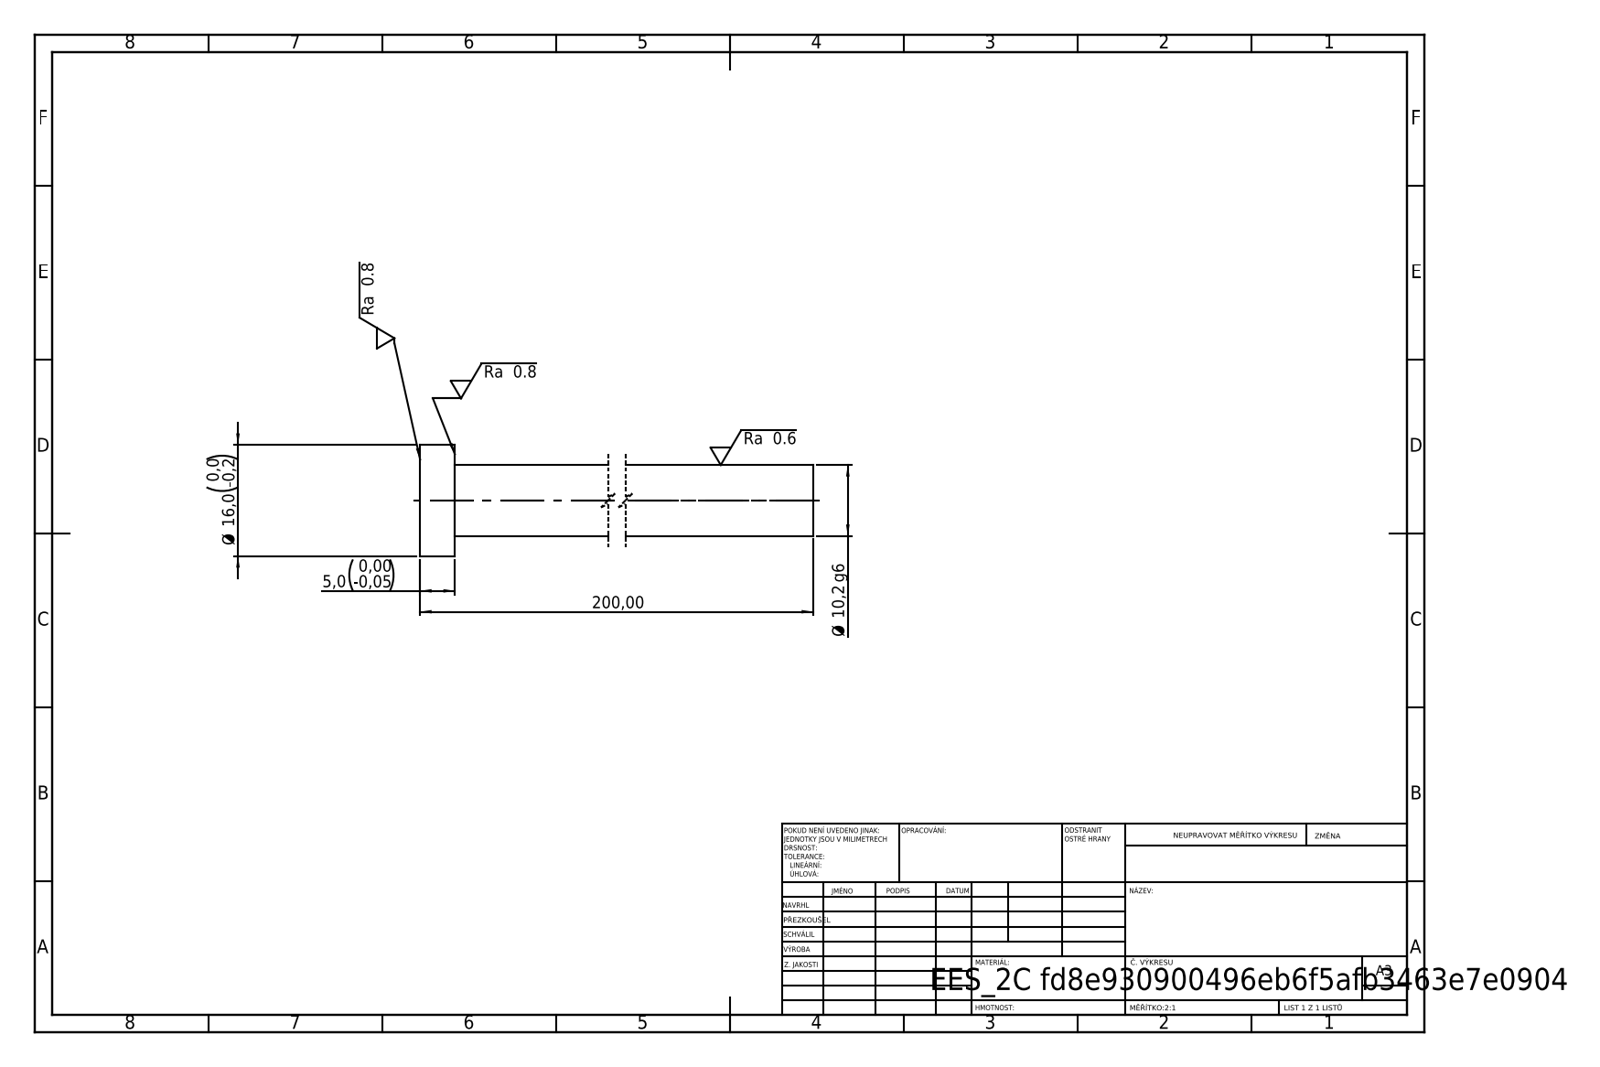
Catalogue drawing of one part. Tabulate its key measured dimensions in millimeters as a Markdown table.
| quantity | value |
| --- | --- |
| STEP written by | SolidWorks 2019 (CONFIG_CONTROL_DESIGN) |
| units | millimeters |
| bodies | 1 solid, 7 faces (3 planar, 4 cylindrical, 0 other) |
| overall size | 200 × 16 × 16 |
| volume | 16 939 mm³ |
| surface area | 6 902 mm² |
| round bosses / shafts (diameter × count) | 16 × 1, 10.2 × 1 |
| main face-to-face distances | 5, 200, 195 |
